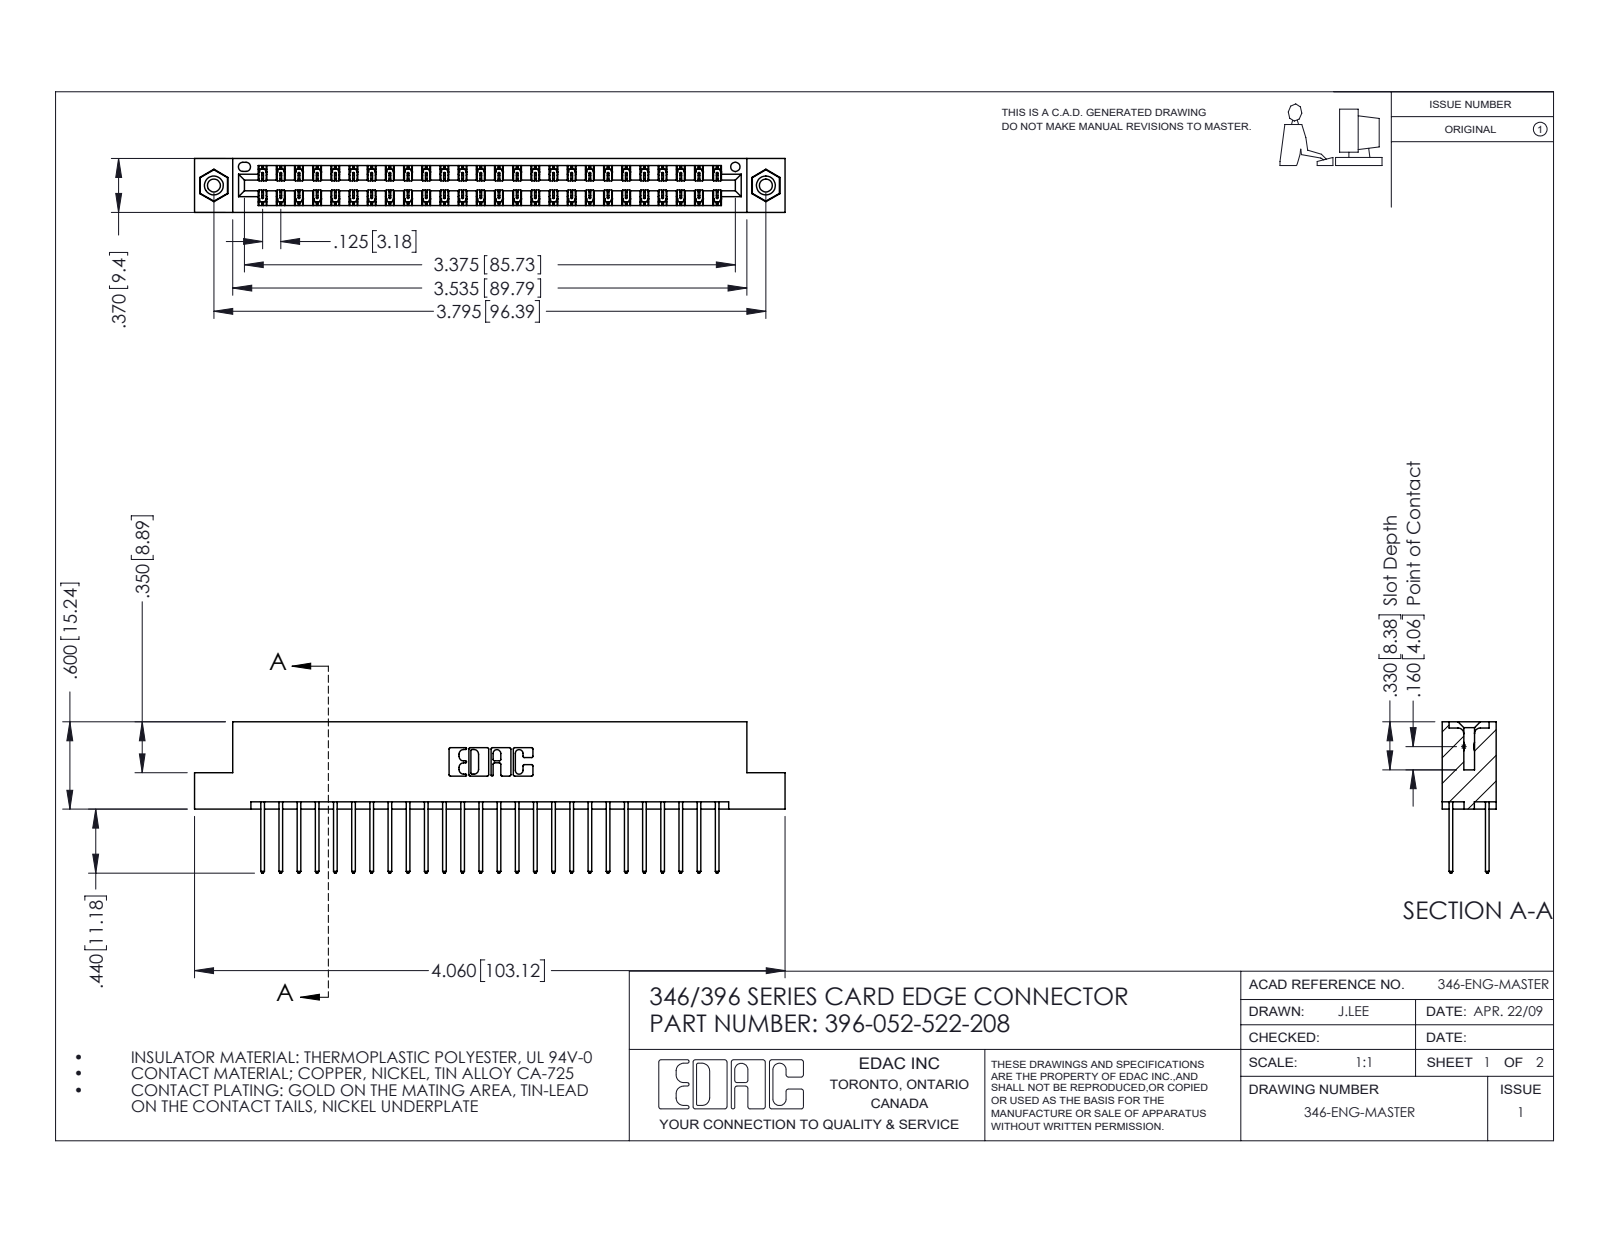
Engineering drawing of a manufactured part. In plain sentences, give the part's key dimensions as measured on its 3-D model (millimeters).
The part is named "345-250-001_345-250-003-102; 396-052-522-208; 346 Part_Flush Mounting Lugs - 0.156 Dia-TI; 345-292-001_345-293-122". Its 3-D file was written by "SolidWorks 2016 (CONFIG_CONTROL_DESIGN)". It is 55 solids with 2886 faces: 1928 planar, 942 cylindrical and 16 other. Overall it measures 103.1 by 26.4 by 9.4 millimeters. Its volume is 10 100 cubic millimeters and its surface area 14 210 square millimeters. Round holes: 2 of diameter 2.3, 2 of diameter 3.2, 2 of diameter 4, 1 of diameter 1.6. Round bosses or shafts: 2 of diameter 3.9. Partial cylindrical surfaces (rounded edges, fillets, slot ends): 78 of radius 0.2, 52 of radius 0.3, 22 of radius 0.3, 6 of radius 0.2, 6 of radius 0.8, 3 of radius 0.7, 2 of radius 0.4, 2 of radius 0.6. The main face-to-face distances are 1.2, 8.2, 6.4, 9.4, 1.8, 7.6, 0.6, 7, 3.8, 5.6. The hole center spacings are 6.2, 91.1, 96.4.
